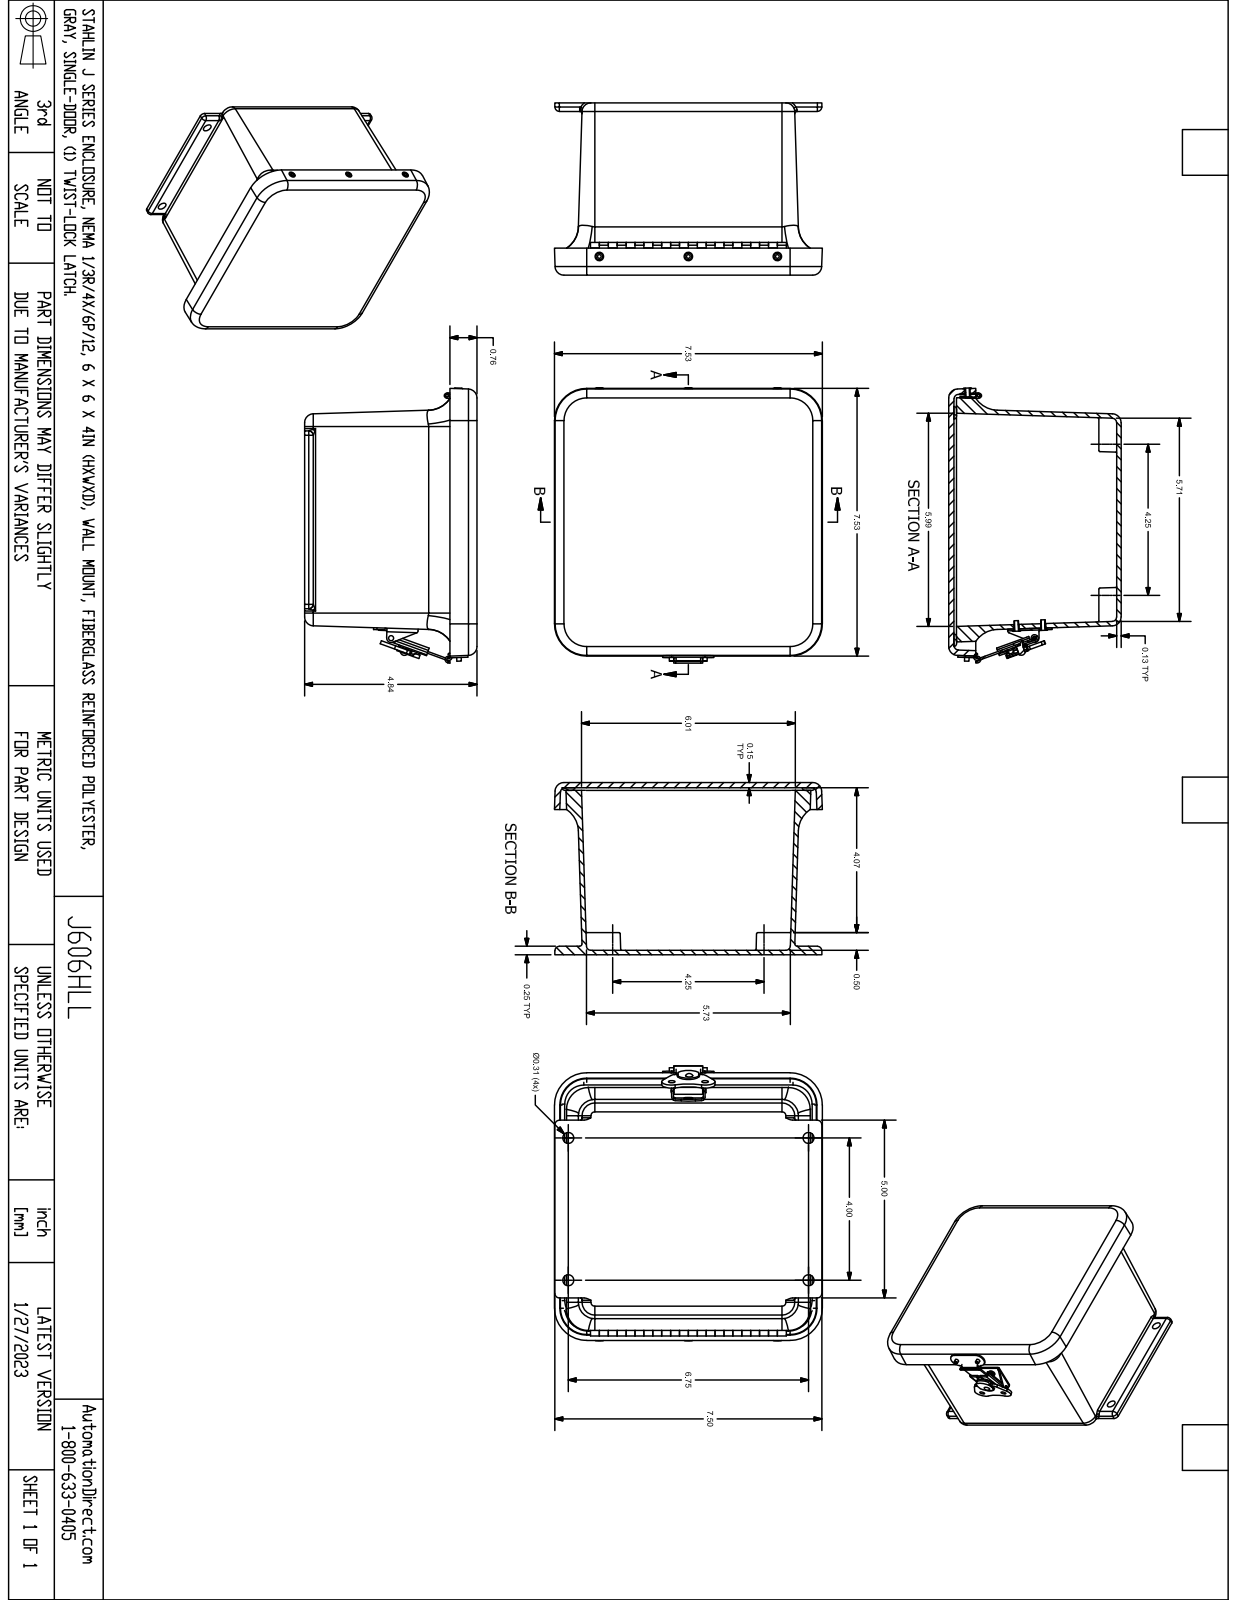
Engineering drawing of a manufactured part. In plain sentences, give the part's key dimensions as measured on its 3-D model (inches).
The part is named "M606HLL". Its 3-D file was written by "SolidWorks 2018 (AUTOMOTIVE_DESIGN)". It is 29 solids with 768 faces: 289 planar, 307 cylindrical and 172 other. Overall it measures 7.809 by 7.525 by 4.838 inches. Its volume is 37.29 cubic inches and its surface area 519.2 square inches. Round holes: 10 of diameter 0.14, 9 of diameter 0.104, 8 of diameter 0.152, 5 of diameter 0.131, 4 of diameter 0.159, 4 of diameter 0.218, 4 of diameter 0.312, 2 of diameter 0.13, 2 of diameter 0.133, 2 of diameter 0.187, 2 of diameter 0.191, 1 of diameter 0.067. Round bosses or shafts: 6 of diameter 0.125, 4 of diameter 0.27, 4 of diameter 0.125, 1 of diameter 0.66, 1 of diameter 0.582, 1 of diameter 0.525, 1 of diameter 0.286, 1 of diameter 0.213. Partial cylindrical surfaces (rounded edges, fillets, slot ends): 36 of radius 0.031, 17 of radius 0.125, 9 of radius 0.25, 8 of radius 0.015, 8 of radius 0.074, 7 of radius 0.06, 4 of radius 0.011, 4 of radius 0.02. The main face-to-face distances are 0.147, 4.691, 4.838, 0.125, 4.566, 4.713, 0.152, 4.5, 4.625, 0.066. The hole center spacings are 2.5, 4.25, 5.308, 4.31, 4, 1.256, 5.502, 1.37.
